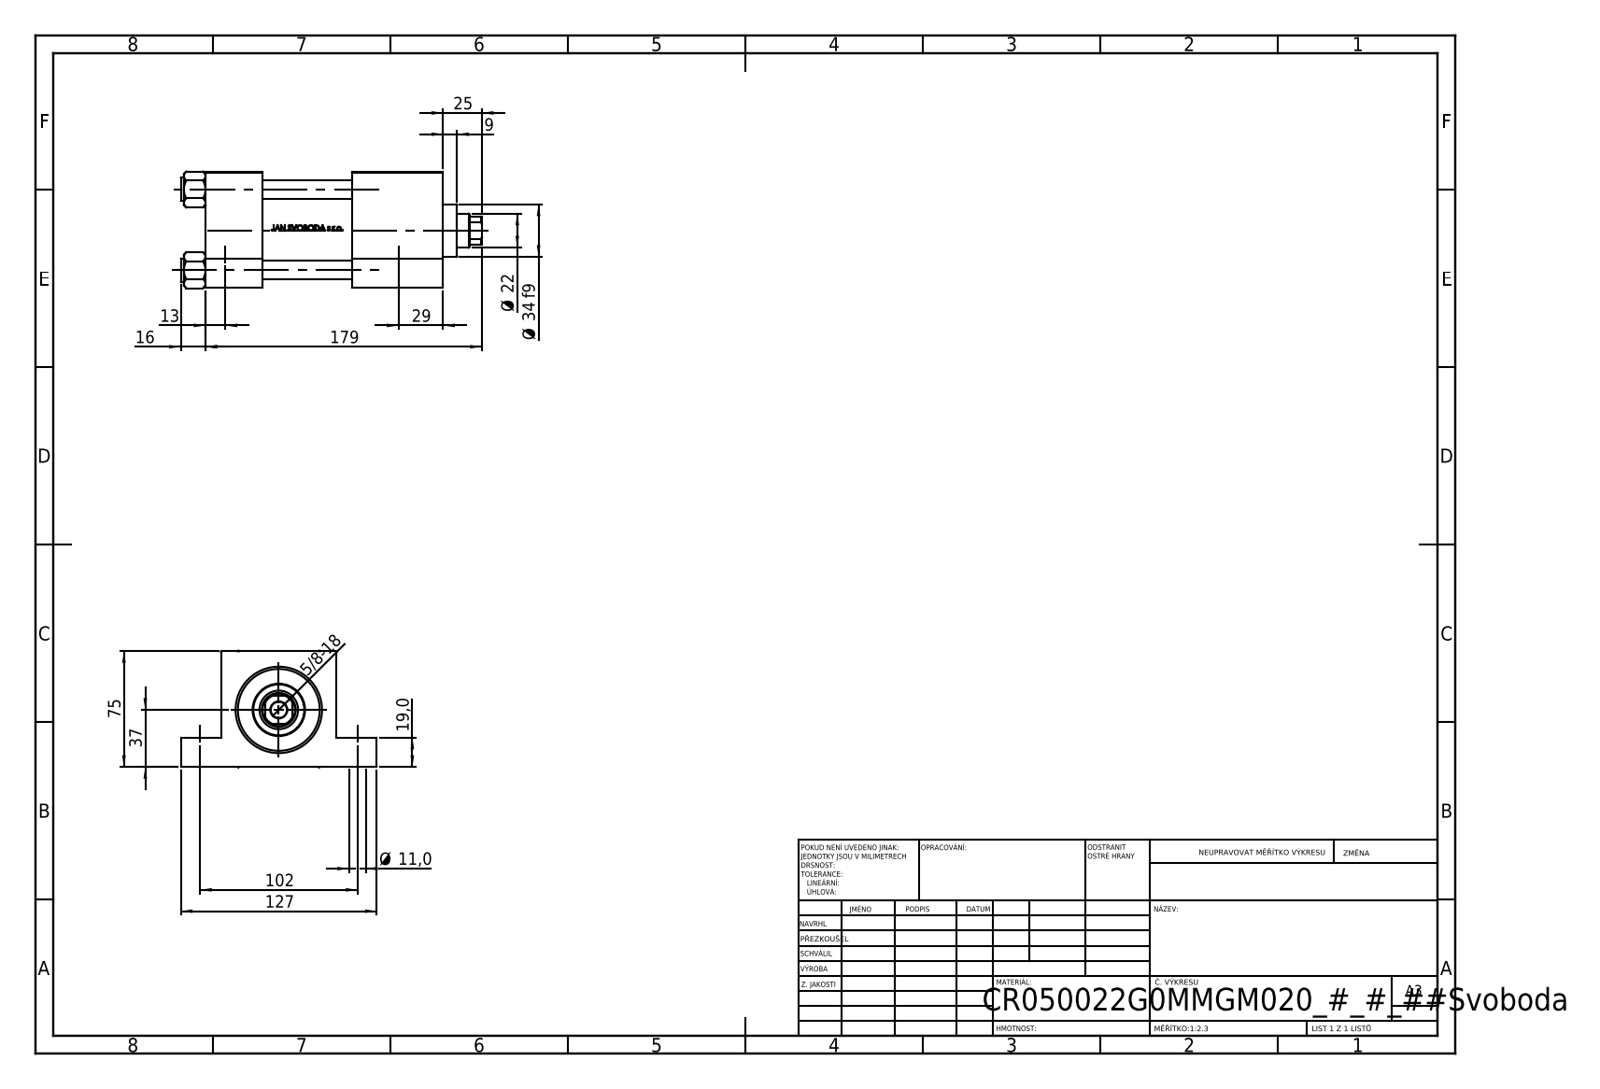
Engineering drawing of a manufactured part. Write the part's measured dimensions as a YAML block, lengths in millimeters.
part_name: "V215CR_G_Body; V215_VC_A; V215CR_VCP_G; V215CR_G_TYCINKA (+1 more)"
step_written_by: "SolidWorks 2019 (CONFIG_CONTROL_DESIGN)"
units: millimeters
bodies: {solids: 11, faces: 1087, planar: 431, cylindrical: 124, other: 532}
overall_size: [195, 127, 75.54]
volume: 755817
surface_area: 159328
round_holes:
  - {diameter: 12, count: 4}
  - {diameter: 11, count: 3}
  - {diameter: 7, count: 2}
  - {diameter: 20.96, count: 2}
  - {diameter: 30, count: 2}
  - {diameter: 10.5, count: 1}
  - {diameter: 11, count: 1}
  - {diameter: 22, count: 1}
  - {diameter: 25, count: 1}
  - {diameter: 41, count: 1}
  - {diameter: 50, count: 1}
  - {diameter: 53, count: 1}
round_bosses_or_shafts:
  - {diameter: 15, count: 4}
  - {diameter: 56, count: 1}
  - {diameter: 34, count: 1}
partial_cylinders:
  - {radius: 10.5, count: 1}
face_to_face_distances: [75, 37, 154, 117, 19, 56, 95, 58, 59, 26]
hole_center_spacings: [52.3, 36.63, 37.34, 73.96, 102, 112, 151.49, 93.5]
